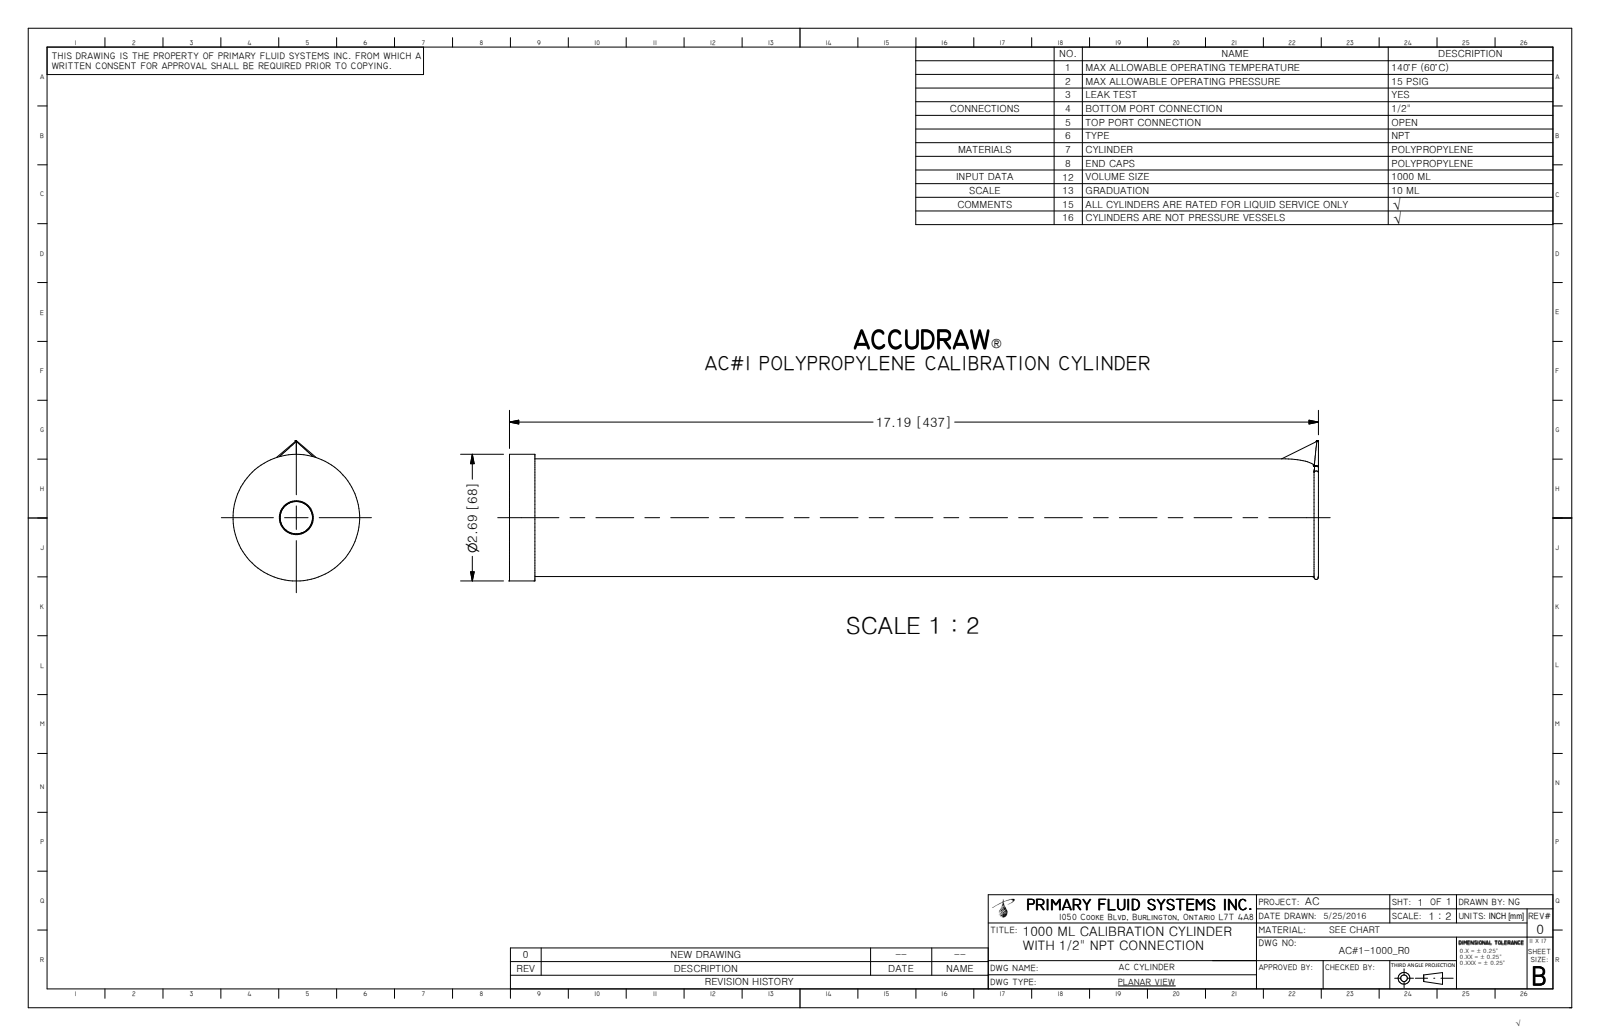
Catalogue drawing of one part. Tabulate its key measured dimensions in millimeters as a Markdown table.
| quantity | value |
| --- | --- |
| part name | AC#1-1000_R0; AC-2B-1000; AC#1-1000-TUBE |
| STEP written by | Autodesk Inventor 2009 (AUTOMOTIVE_DESIGN) |
| units | millimeters |
| bodies | 2 solids, 24 faces (10 planar, 4 cylindrical, 10 other) |
| overall size | 436.6 × 75.7 × 68.3 |
| volume | 252 000 mm³ |
| surface area | 175 700 mm² |
| round holes (diameter × count) | 58.8 × 1 |
| round bosses / shafts (diameter × count) | 68.3 × 1, 63.5 × 1, 57.9 × 1 |
| main face-to-face distances | 19.1, 13.7, 5.3, 436.6, 422.9, 417.6, 434.3, 420.6, 415.2, 2.3 |
